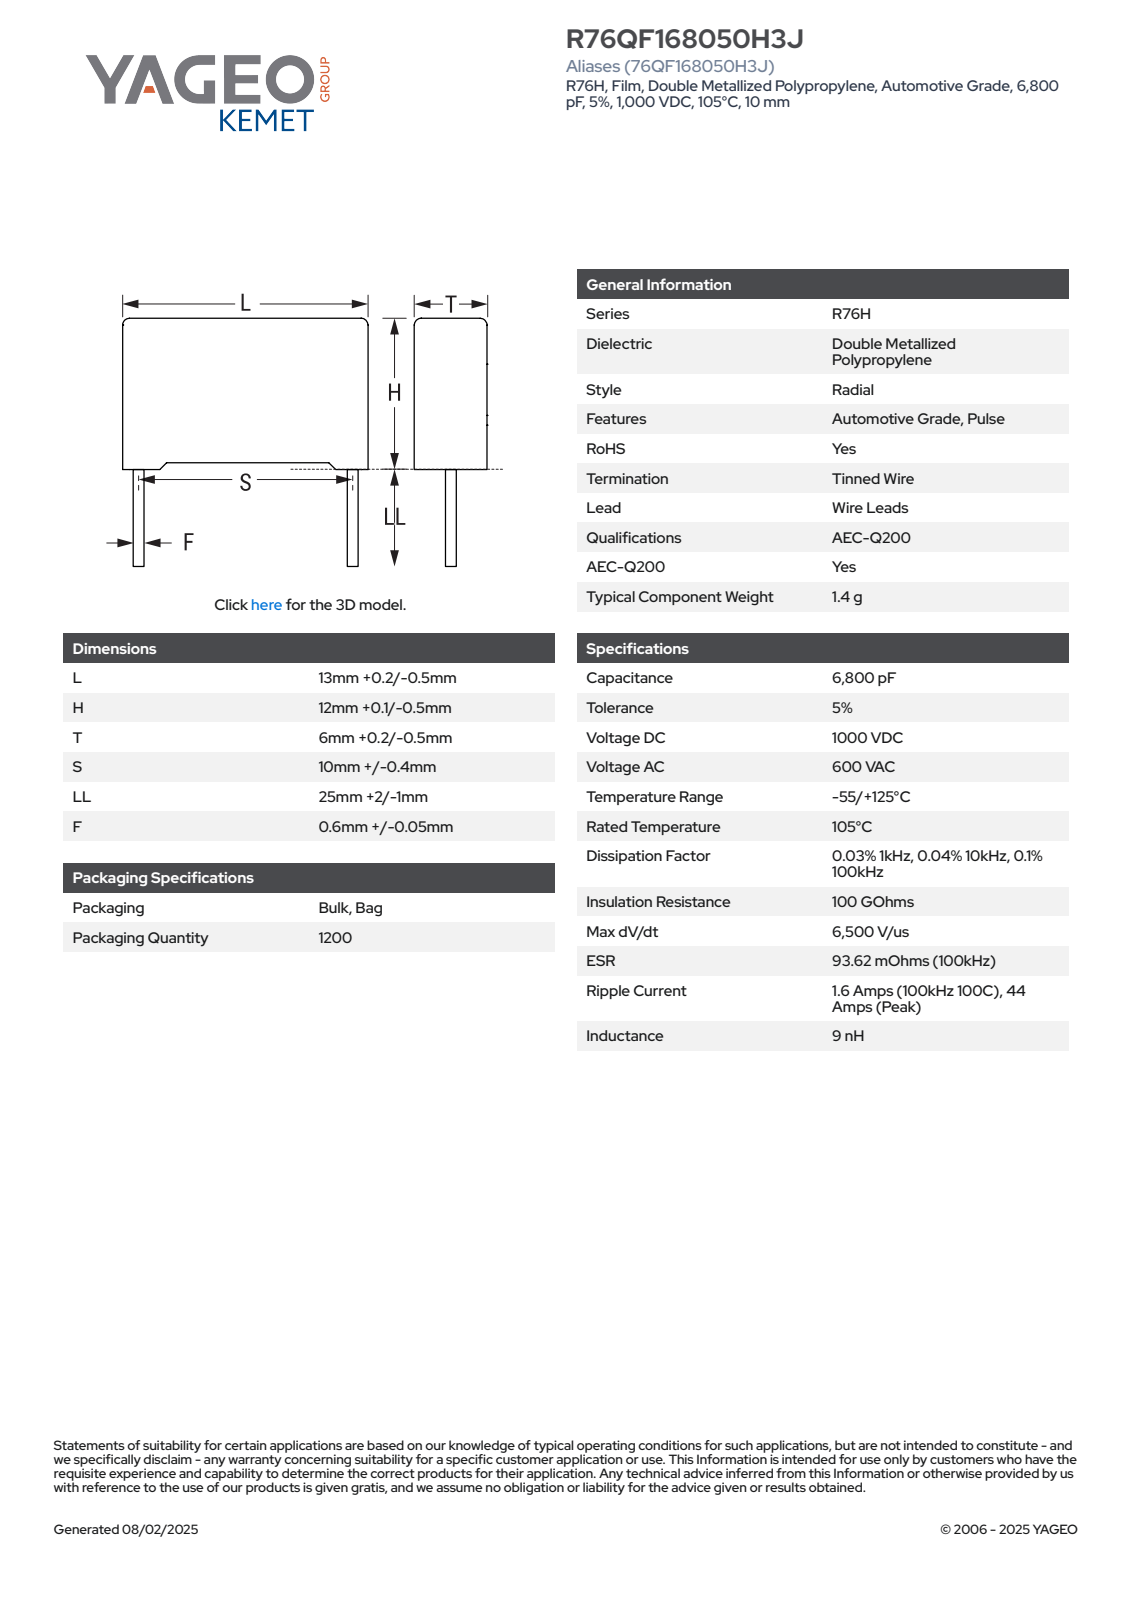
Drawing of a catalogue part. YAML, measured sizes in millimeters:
part_name: "CFR_RB2R76_13X12X6_L13.2H12.1T6.2S10LL27F0.65"
step_written_by: "SolidWorks 2014 (AUTOMOTIVE_DESIGN)"
units: millimeters
bodies: {solids: 4, faces: 85, planar: 77, cylindrical: 8, other: 0}
overall_size: [39.1, 13.2, 6.21]
volume: 955
surface_area: 767
round_bosses_or_shafts:
  - {diameter: 0.65, count: 2}
partial_cylinders:
  - {radius: 0.5, count: 4}
face_to_face_distances: [6.2, 13.2, 11.35, 0.44, 5.76, 0.75, 12.1, 12.76, 5.32, 0.42]
